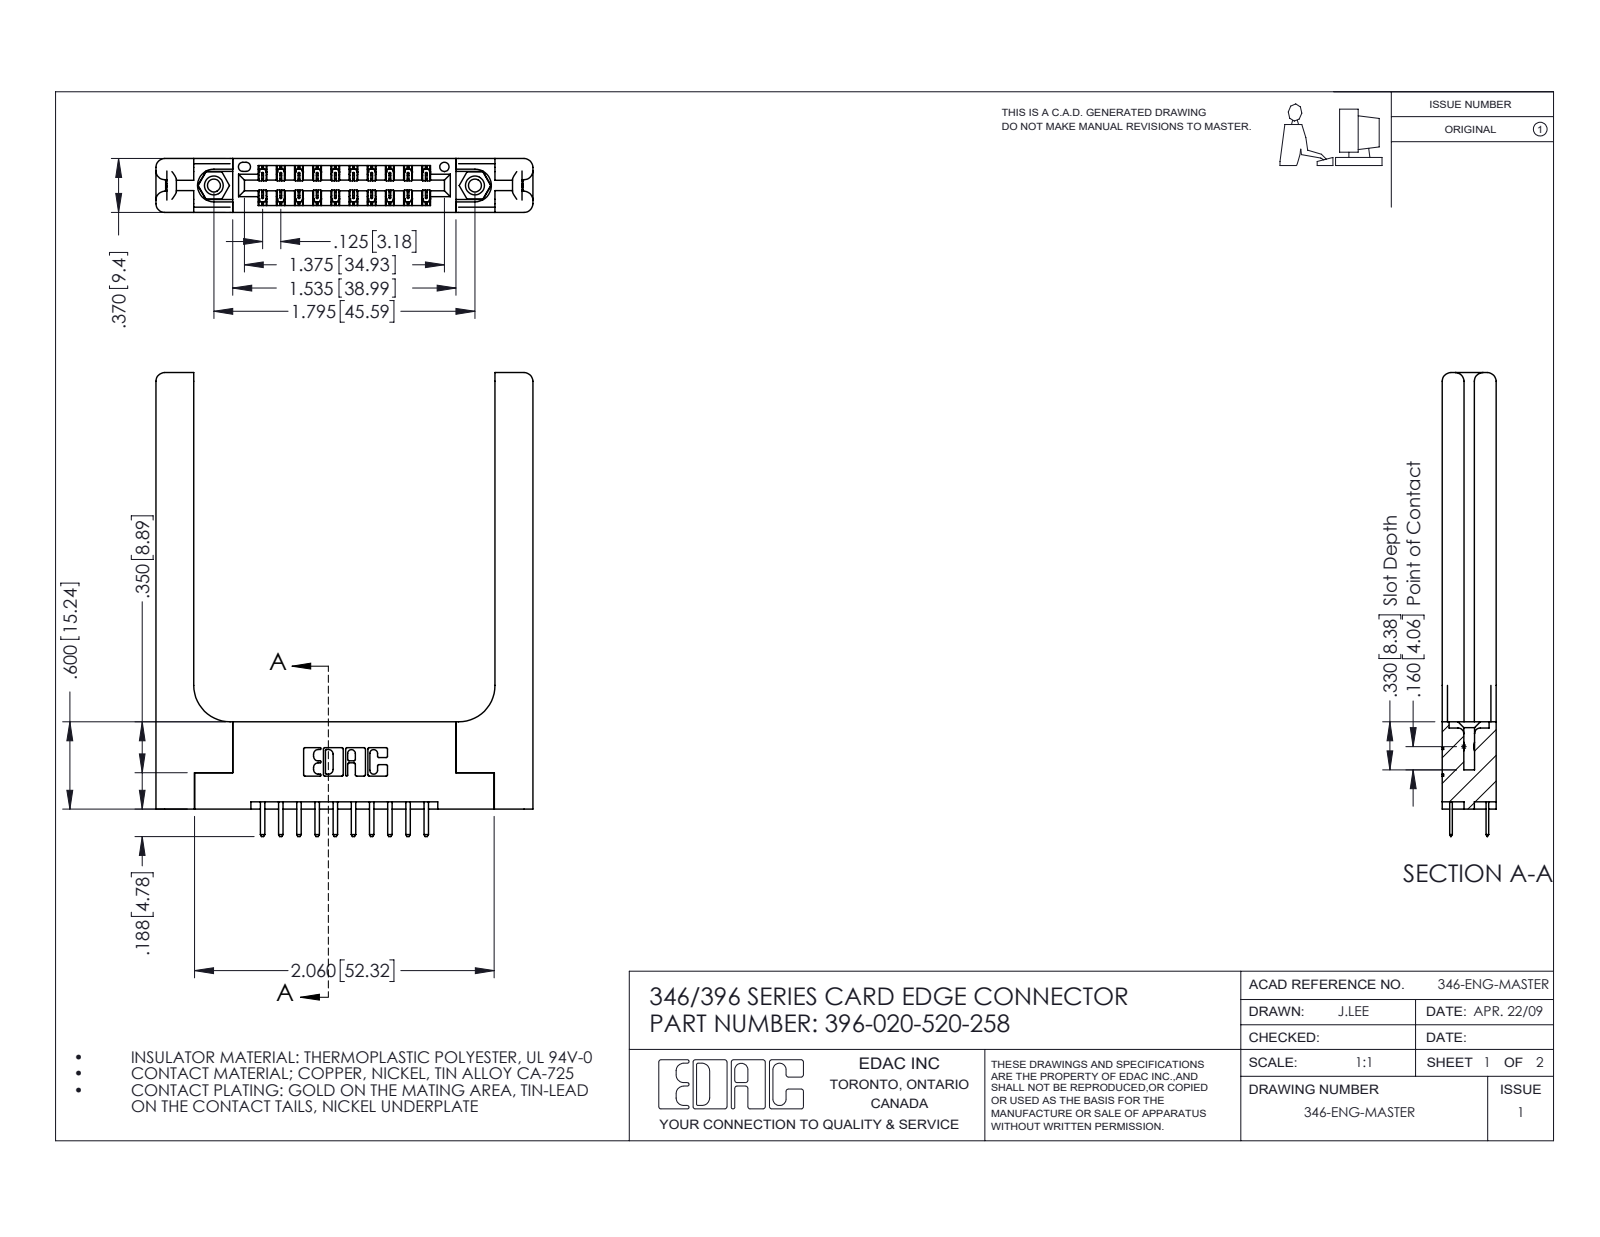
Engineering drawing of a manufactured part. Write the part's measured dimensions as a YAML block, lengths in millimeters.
part_name: "346 Part_Flush Mounting Lugs - 0.156 Dia-TH; 396-020-520-258; 346-220-058_345-220-058; 345-292-001_345-293-120 (+1 more)"
step_written_by: "SolidWorks 2016 (CONFIG_CONTROL_DESIGN)"
units: millimeters
bodies: {solids: 25, faces: 1498, planar: 964, cylindrical: 474, other: 60}
overall_size: [81, 65.8, 9.4]
volume: 13700
surface_area: 12920
round_holes:
  - {diameter: 2.3, count: 2}
  - {diameter: 3.2, count: 2}
  - {diameter: 4, count: 2}
  - {diameter: 1.6, count: 1}
round_bosses_or_shafts:
  - {diameter: 3.9, count: 2}
partial_cylinders:
  - {radius: 0.2, count: 30}
  - {radius: 0.3, count: 24}
  - {radius: 0.3, count: 22}
  - {radius: 1.5, count: 16}
  - {radius: 0.2, count: 6}
  - {radius: 0.8, count: 6}
  - {radius: 0.7, count: 3}
  - {radius: 0.4, count: 2}
face_to_face_distances: [9.4, 3.8, 1.8, 5.6, 6.4, 3.8, 2.6, 1.2, 8.2, 4.4]
hole_center_spacings: [6.2, 40.4, 45.6]
